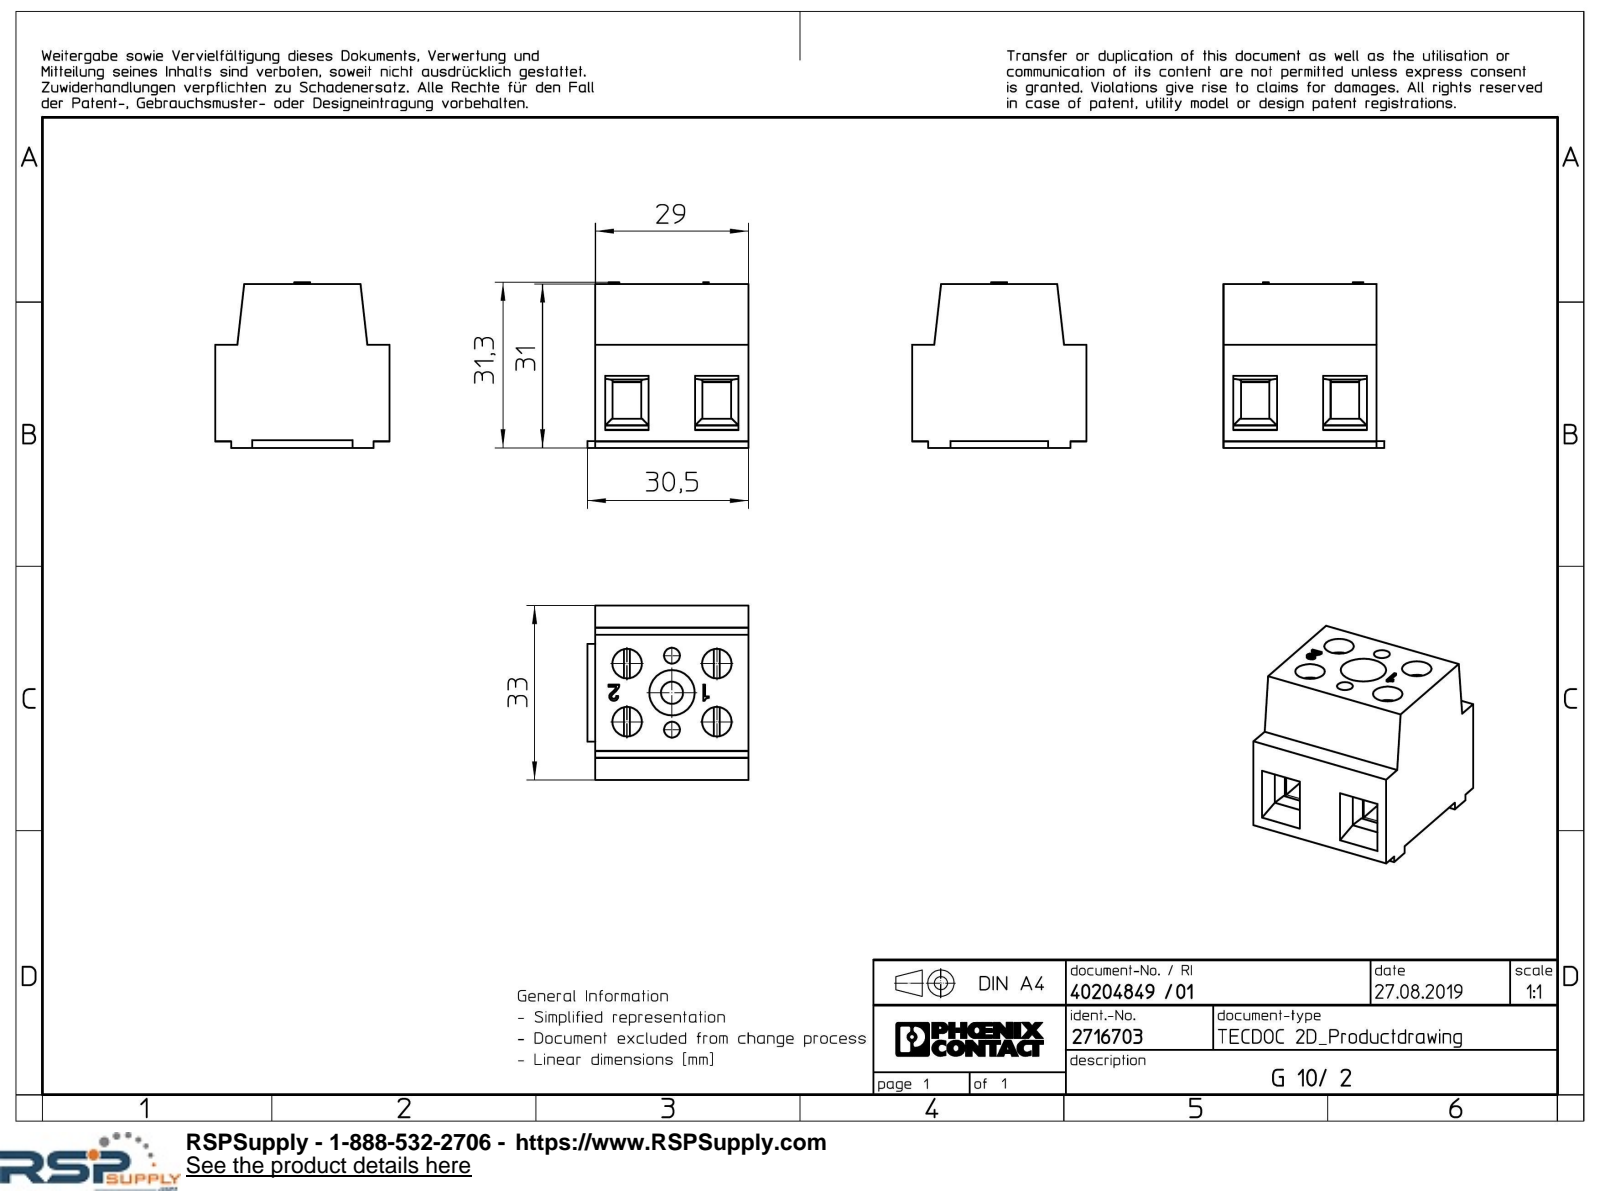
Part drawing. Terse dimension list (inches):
name: G_10_2-select
written by: Creo Elements/Direct Modeling 20.1A 29-Sep-2018 (C) Parametric Technology GmbH (AUTOMOTIVE_DESIGN)
unit: in
bodies: 1 solid, 185 faces (169 planar, 16 cylindrical, 0 other)
size: 1.299 × 1.232 × 1.201
volume: 1.308 in³; area: 12.72 in²
holes: 4× ⌀0.22, 2× ⌀0.118, 1× ⌀0.165, 1× ⌀0.339
face distances: 1.142, 1.22, 1.299, 0.669, 0.343, 0.799, 0.13, 1.012, 0.213, 0.768
hole spacings: 0.34, 0.398, 0.595, 0.276, 0.433, 0.669, 0.797, 0.551
